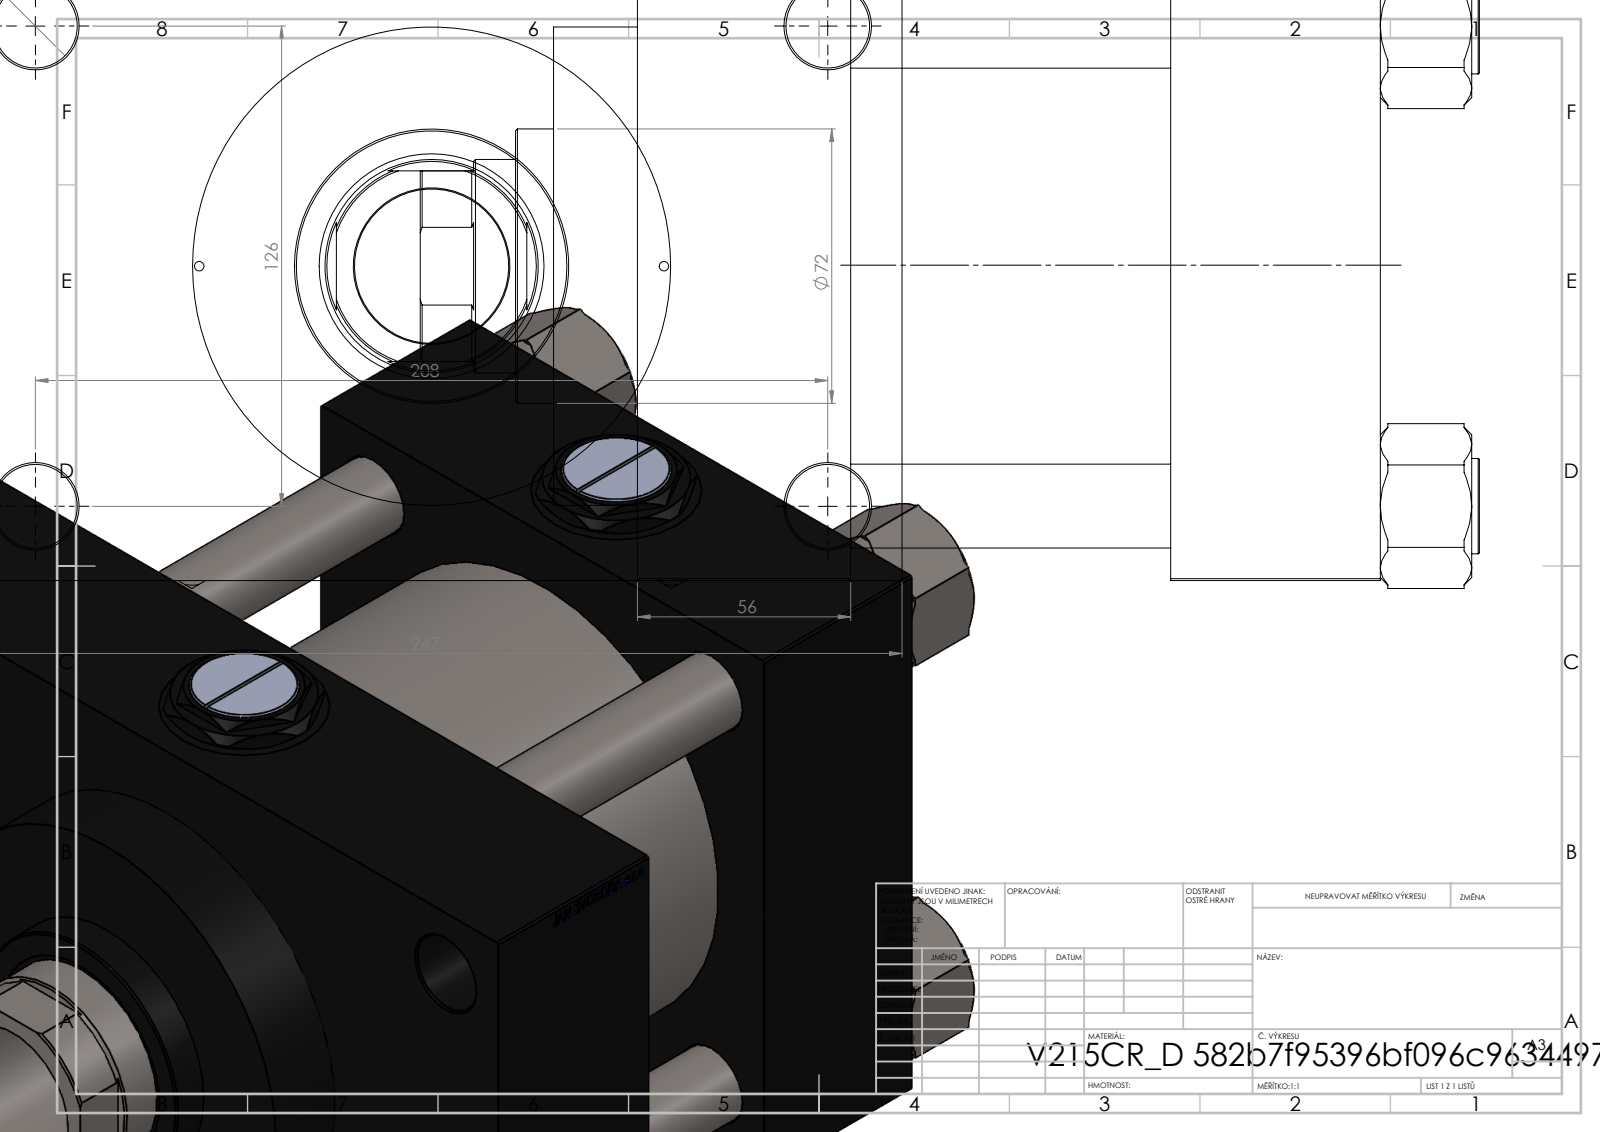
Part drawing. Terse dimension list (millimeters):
name: V215CR_D_Body; NUT_M5_D; V215CR_VCP_D; V215CR_D_TYCINKA (+2 more)
written by: SolidWorks 2019 (CONFIG_CONTROL_DESIGN)
unit: mm
bodies: 13 solids, 1255 faces (594 planar, 101 cylindrical, 560 other)
size: 278 × 247 × 174.07
volume: 4 902 000 mm³; area: 544 413 mm²
holes: 8× ⌀22, 4× ⌀32.24, 4× ⌀45, 3× ⌀7, 2× ⌀2.5, 1× ⌀40.5, 1× ⌀56, 1× ⌀59, 1× ⌀96, 1× ⌀125, 1× ⌀125.5
bosses: 4× ⌀25, 1× ⌀131, 1× ⌀72
rounds: 1× R27
face distances: 84, 165, 55, 139, 56, 195, 140, 41, 206, 173.74
hole spacings: 41.05, 62.98, 76.28, 89.02, 121.59, 125.9, 132.47, 139.02
